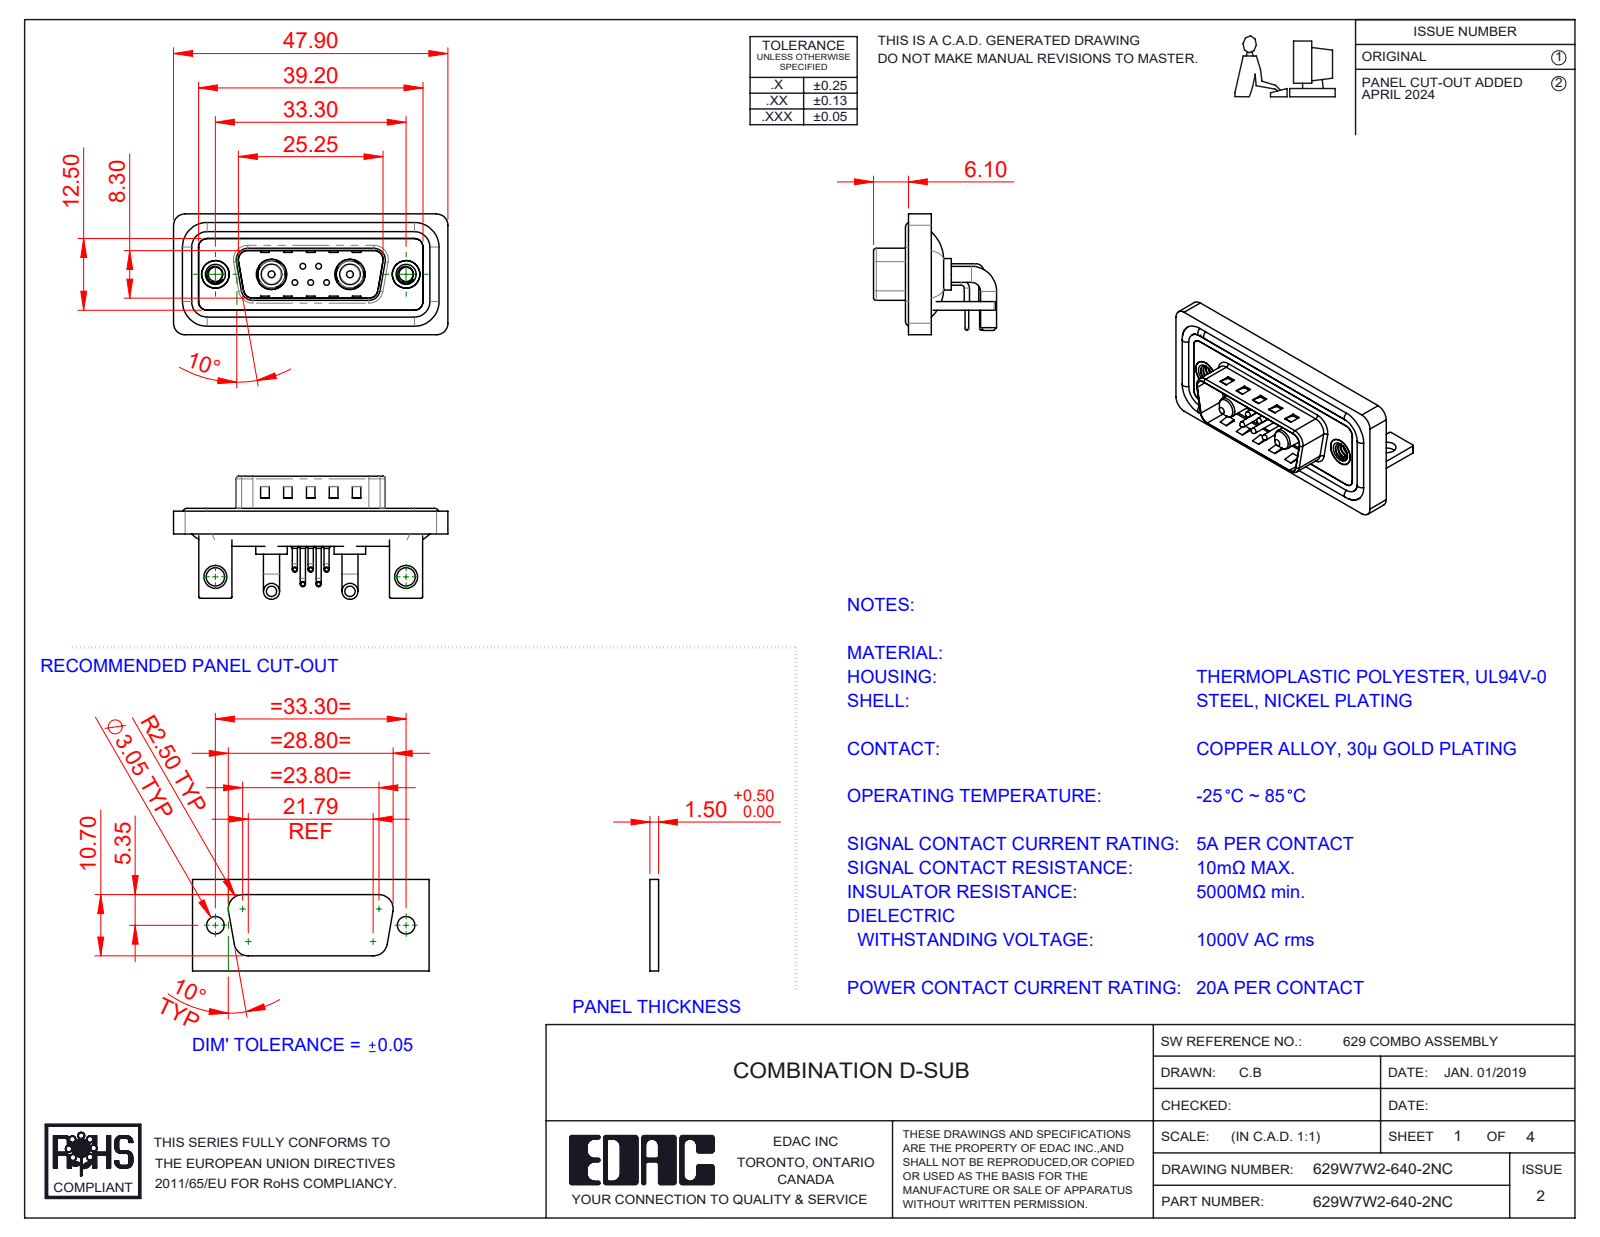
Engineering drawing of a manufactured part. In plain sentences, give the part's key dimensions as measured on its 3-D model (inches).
The part is named "629Combo Contact Row 2; 629Combo Stabilizer Bracket; 629Combo Waterproof Housing_15 Contacts; 629Combo Housing_7W2 (+6 more)". Its 3-D file was written by "SolidWorks 2023 (CONFIG_CONTROL_DESIGN)". It is 18 solids with 1121 faces: 537 planar, 424 cylindrical and 160 other. Overall it measures 1.886 by 0.846 by 0.831 inches. Its volume is 0.363 cubic inches and its surface area 15.08 square inches. Round holes: 5 of diameter 0.03, 5 of diameter 0.063, 5 of diameter 0.079, 2 of diameter 0.098, 2 of diameter 0.126, 2 of diameter 0.157, 2 of diameter 0.189, 2 of diameter 0.191, 2 of diameter 0.197, 2 of diameter 0.209. Round bosses or shafts: 10 of diameter 0.035, 5 of diameter 0.059, 5 of diameter 0.039, 5 of diameter 0.026, 4 of diameter 0.11, 4 of diameter 0.063, 2 of diameter 0.217, 2 of diameter 0.205. Partial cylindrical surfaces (rounded edges, fillets, slot ends): 21 of radius 0.079, 18 of radius 0.059, 16 of radius 0.01, 9 of radius 0.02, 8 of radius 0.063, 5 of radius 0.04, 4 of radius 0.024, 4 of radius 0.026. The main face-to-face distances are 0.016, 0.059, 0.031, 0.114, 0.083, 0.043, 0.063, 0.047, 0.146, 0.177. The hole center spacings are 0.124, 0.109, 0.386, 0.925, 1.311, 0.17, 0.17, 0.198.
